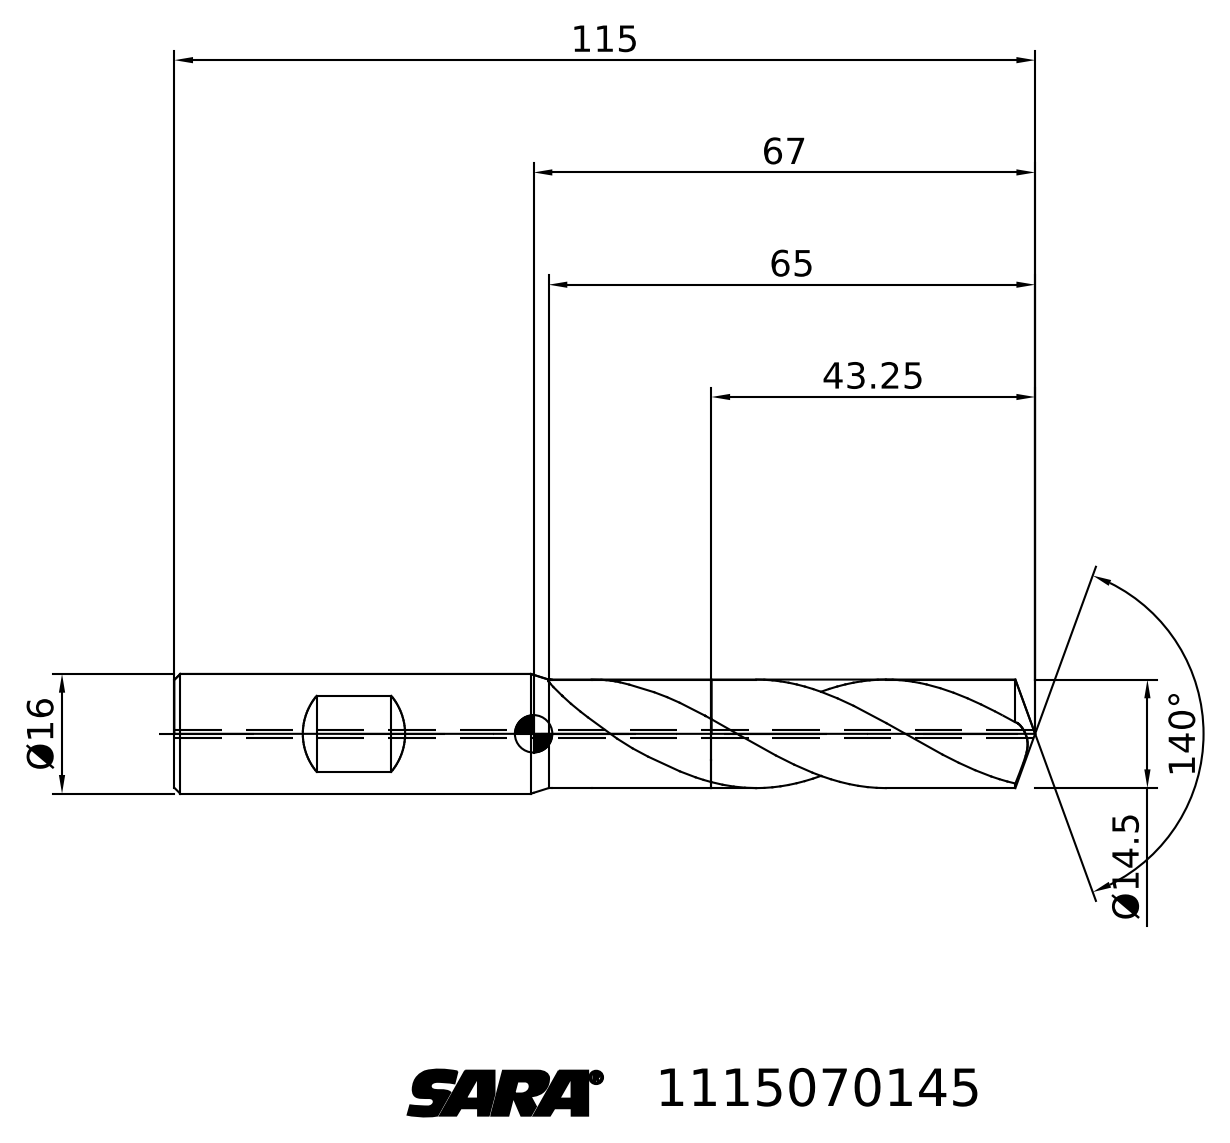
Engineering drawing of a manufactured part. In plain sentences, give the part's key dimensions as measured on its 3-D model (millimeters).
Its 3-D file was written by "TDM (AUTOMOTIVE_DESIGN)". It is 2 solids with 30 faces: 6 planar, 0 cylindrical and 24 other. Overall it measures 115 by 16.59 by 16 millimeters. Its volume is 16 974 cubic millimeters and its surface area 6 134 square millimeters. The main face-to-face distances are 71.75.
